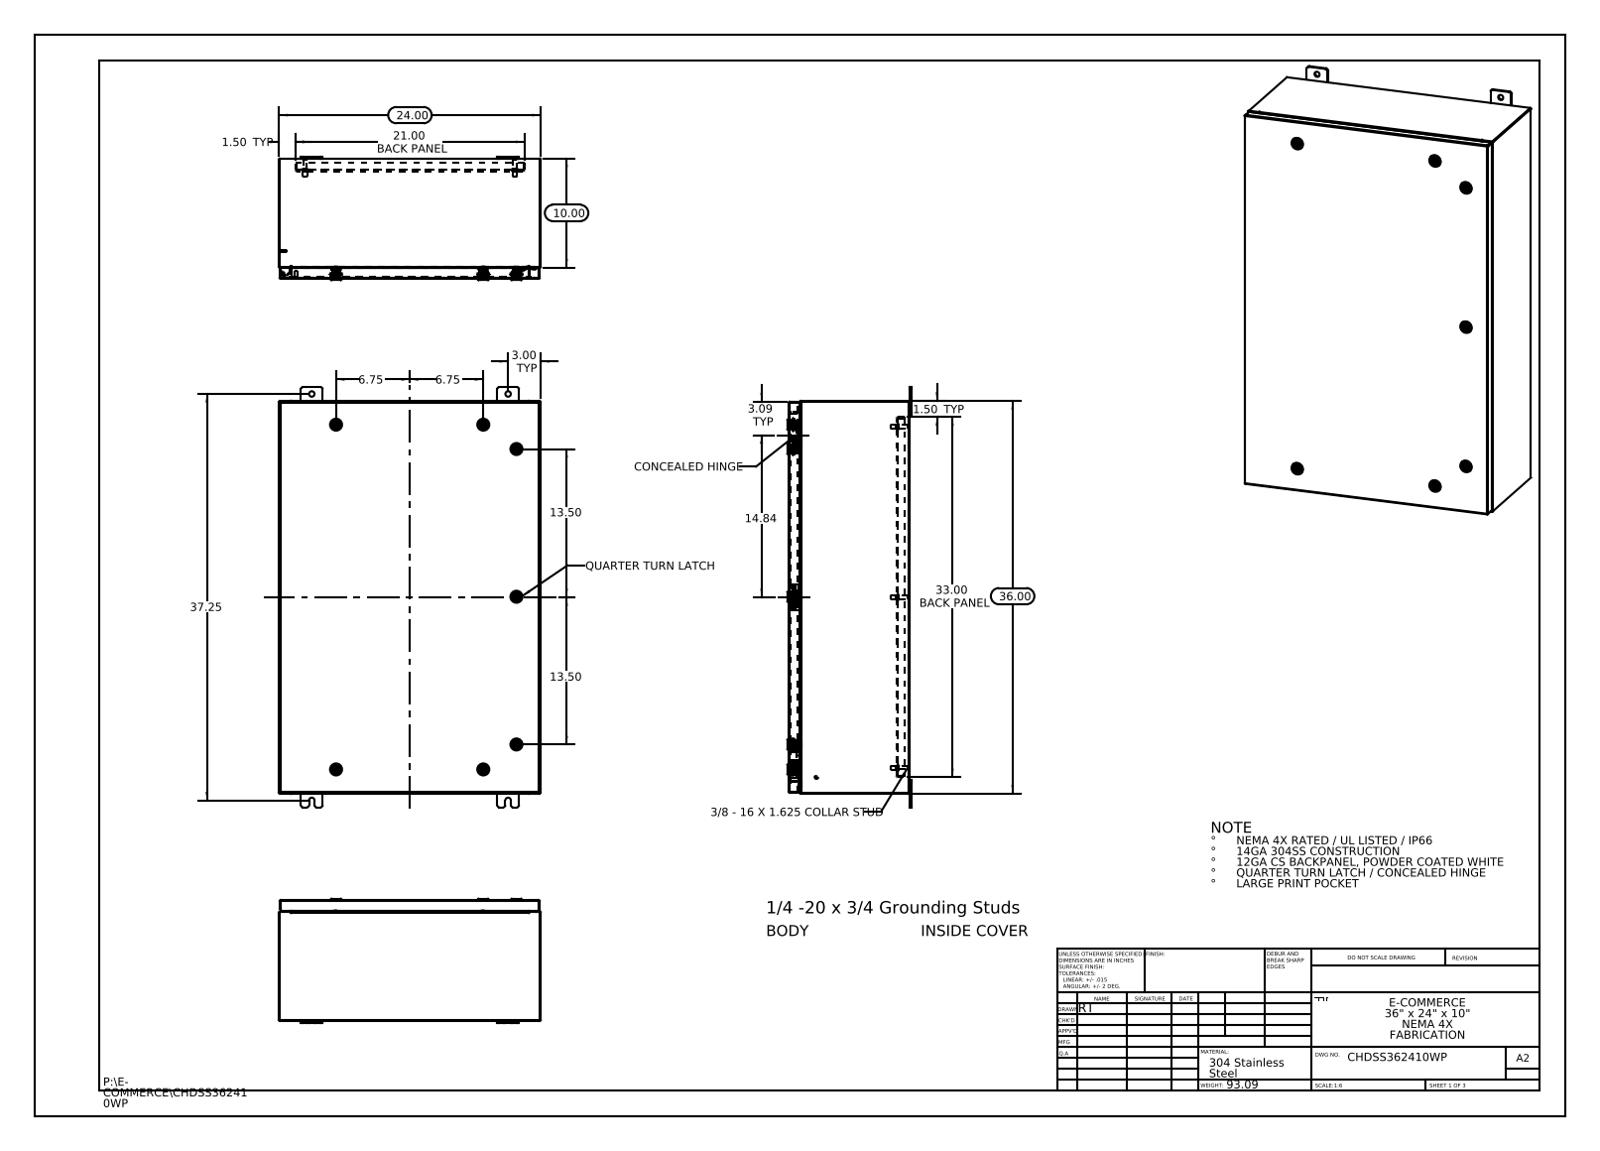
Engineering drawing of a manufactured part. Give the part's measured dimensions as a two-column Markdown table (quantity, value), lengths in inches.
| quantity | value |
| --- | --- |
| part name | CHDSS362410WP Mounting Feet; Screw-221320-IB-Industrilas_Screw-221320-IB-Industrilas; CHDSS362410WP Top; HW-CLH-R001-0500_2412-026240-2445-Industrilas (+8 more) |
| STEP written by | SolidWorks 2013 (CONFIG_CONTROL_DESIGN) |
| units | inches |
| bodies | 65 solids, 6356 faces (1866 planar, 1988 cylindrical, 2502 other) |
| overall size | 38.5 × 24 × 11.356 |
| volume | 330.4 in³ |
| surface area | 8 218 in² |
| round holes (diameter × count) | 0.5 × 10, 0.197 × 7, 0.394 × 7, 0.4 × 7, 0.63 × 7, 0.787 × 7, 0.136 × 6, 0.211 × 1 |
| round bosses / shafts (diameter × count) | 0.236 × 9, 1.102 × 7, 0.78 × 7, 0.626 × 7, 0.61 × 7, 0.531 × 7, 0.392 × 7, 0.114 × 7 |
| partial cylindrical surfaces (radius × count) | 0.006 × 231, 0.118 × 231, 0.028 × 84, 0.02 × 28, 0.197 × 28, 0.19 × 24, 0.013 × 22, 0.088 × 18 |
| main face-to-face distances | 0.075, 0.074, 11.01, 10.935, 10.936, 10.861, 0.104, 23.925, 1, 1.075 |
| hole center spacings | 15.625, 24.793, 19.25, 0.688, 1.858, 3.065, 13.5, 14.156 |
